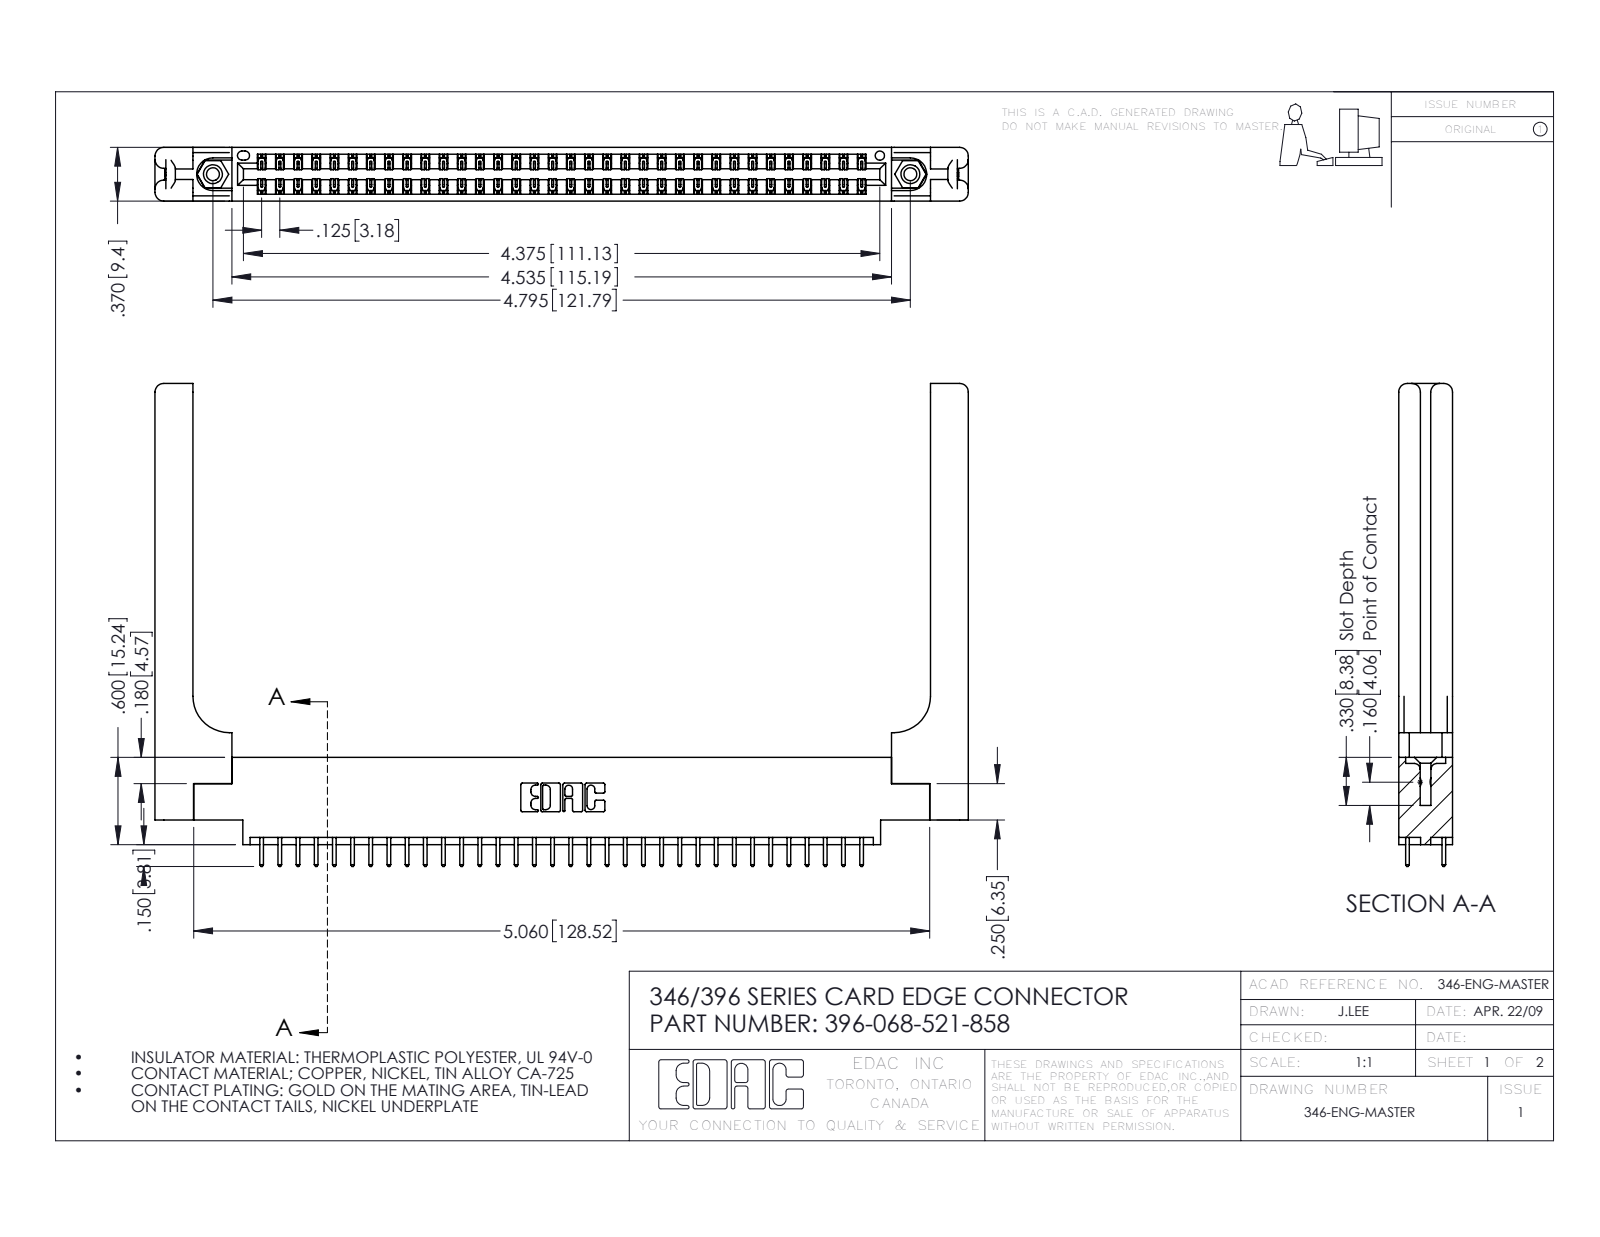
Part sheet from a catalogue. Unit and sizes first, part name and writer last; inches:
Units: inches
Overall size (bounding box): 5.591 × 3.32 × 0.37
Round holes (diameter × count): ⌀0.089 ×2, ⌀0.125 ×2, ⌀0.156 ×2, ⌀0.064 ×1
Round bosses / shafts (diameter × count): ⌀0.155 ×2
Partial cylindrical surfaces — rounded edges, fillets, slot ends (radius × count): R0.006 ×102, R0.01 ×68, R0.01 ×22, R0.06 ×16, R0.007 ×6, R0.031 ×6, R0.026 ×3, R0.014 ×2
Main face-to-face distances: 0.37, 0.048, 0.322, 0.072, 0.148, 0.15, 0.25, 0.025, 0.298, 0.275
Hole centre spacings: 0.246, 4.587, 4.795
Volume: 1.287 in³ · Surface area: 36.48 in²
Bodies: 73 solids, 3918 faces (2608 planar, 1250 cylindrical, 60 other)
Part name (STEP PRODUCT): 346 Part_0.170 Offset - 0.156 Dia-TH; 345-250-001_345-250-001-102; 396-068-521-858; 346-220-058_345-220-058 (+1 more)
STEP written by: SolidWorks 2016 (CONFIG_CONTROL_DESIGN)
